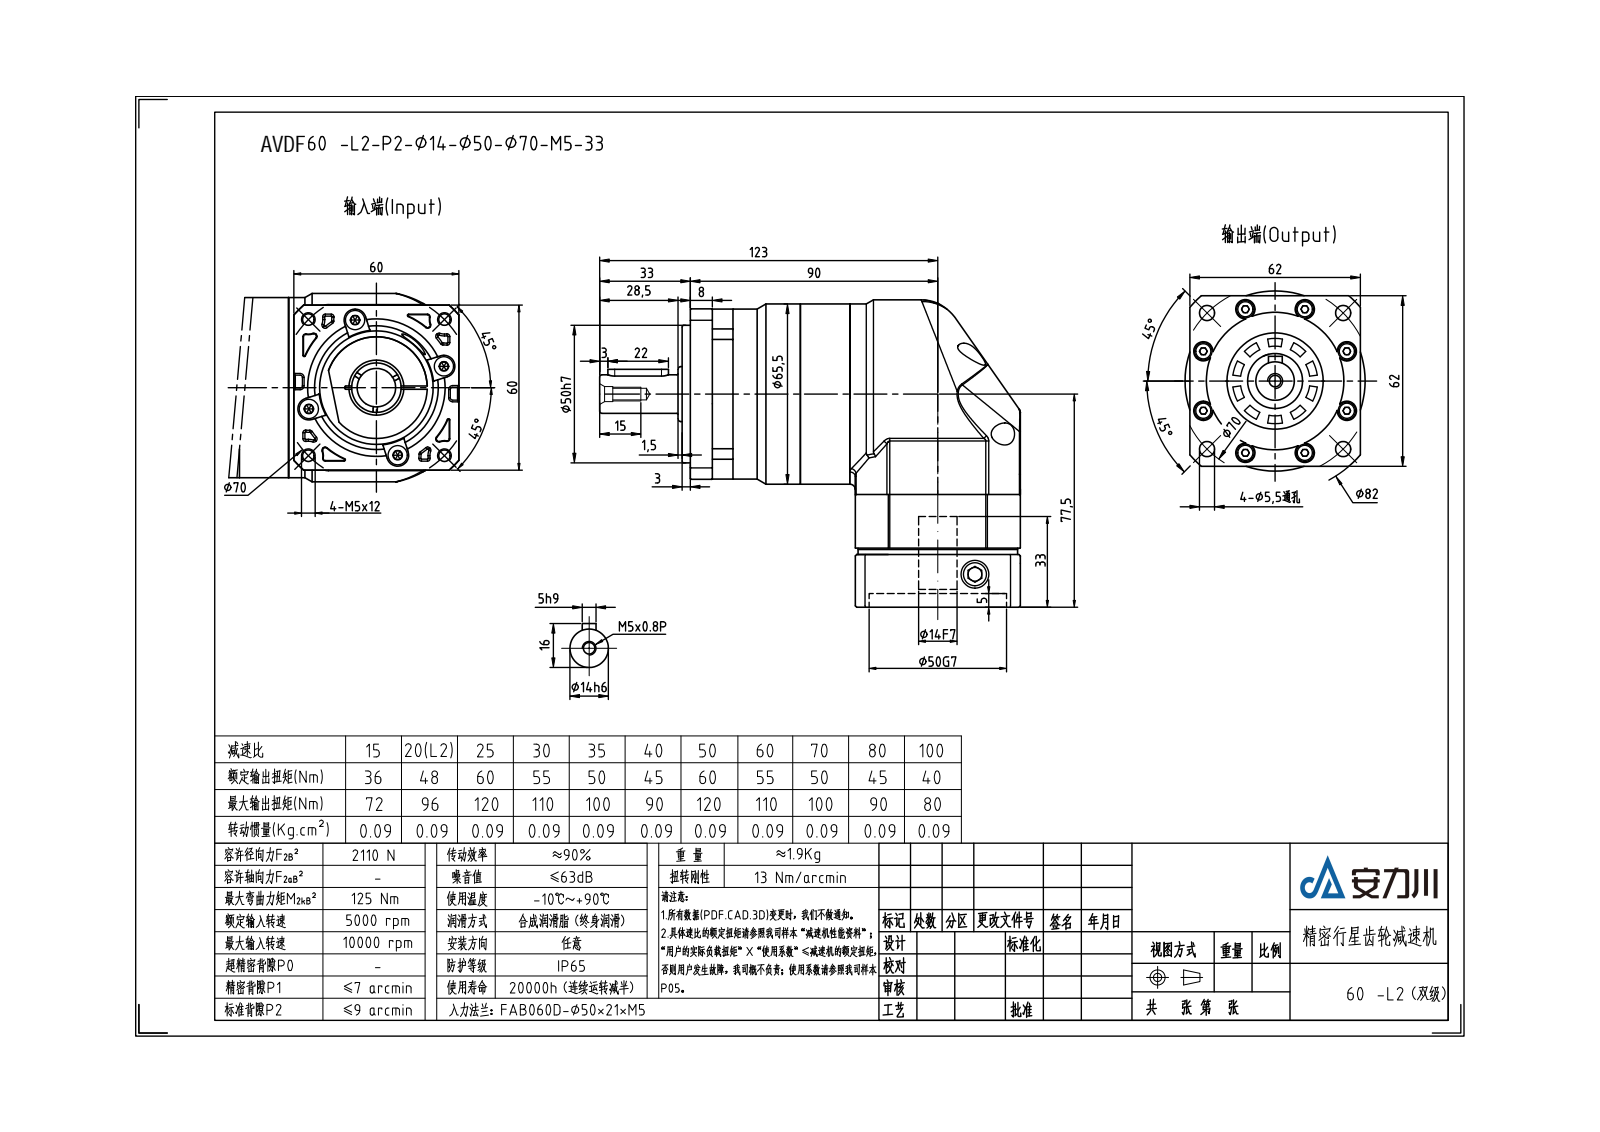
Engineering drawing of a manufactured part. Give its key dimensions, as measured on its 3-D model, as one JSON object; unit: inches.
{"part_name": "FGA060D-L2-前段; FADR064-后端-14-50-70-M4-33; FGAR060D-L2-P2-14-50-70-M5-33", "step_written_by": "SolidWorks 2018 (CONFIG_CONTROL_DESIGN)", "units": "inches", "bodies": {"solids": 28, "faces": 1524, "planar": 486, "cylindrical": 484, "other": 554}, "overall_size": [7.165, 4.4, 2.697], "volume_in3": 30.83, "surface_area_in2": 220.7, "round_holes": [[0.13, 22], [0.177, 15], [0.217, 6], [0.295, 6], [0.173, 5], [0.315, 5], [0.354, 2], [1.378, 2], [1.575, 2], [0.165, 1], [0.169, 1], [0.335, 1]], "round_bosses_or_shafts": [[0.217, 8], [0.118, 8], [0.276, 5], [0.26, 5], [0.157, 5], [0.551, 2], [2.579, 1], [2.433, 1]], "partial_cylinders_radius": [[0.012, 32], [0.02, 12], [0.079, 11], [0.039, 8], [0.157, 4], [0.197, 4], [1.476, 3], [0.016, 2]], "face_to_face_distances": [1.142, 0.118, 0.787, 0.846, 0.728, 2.362, 2.106, 0.965, 2.114, 0.709], "hole_center_spacings": [1.142, 0.552, 0.851, 1.112, 1.378, 1.401, 1.573, 1.949]}
